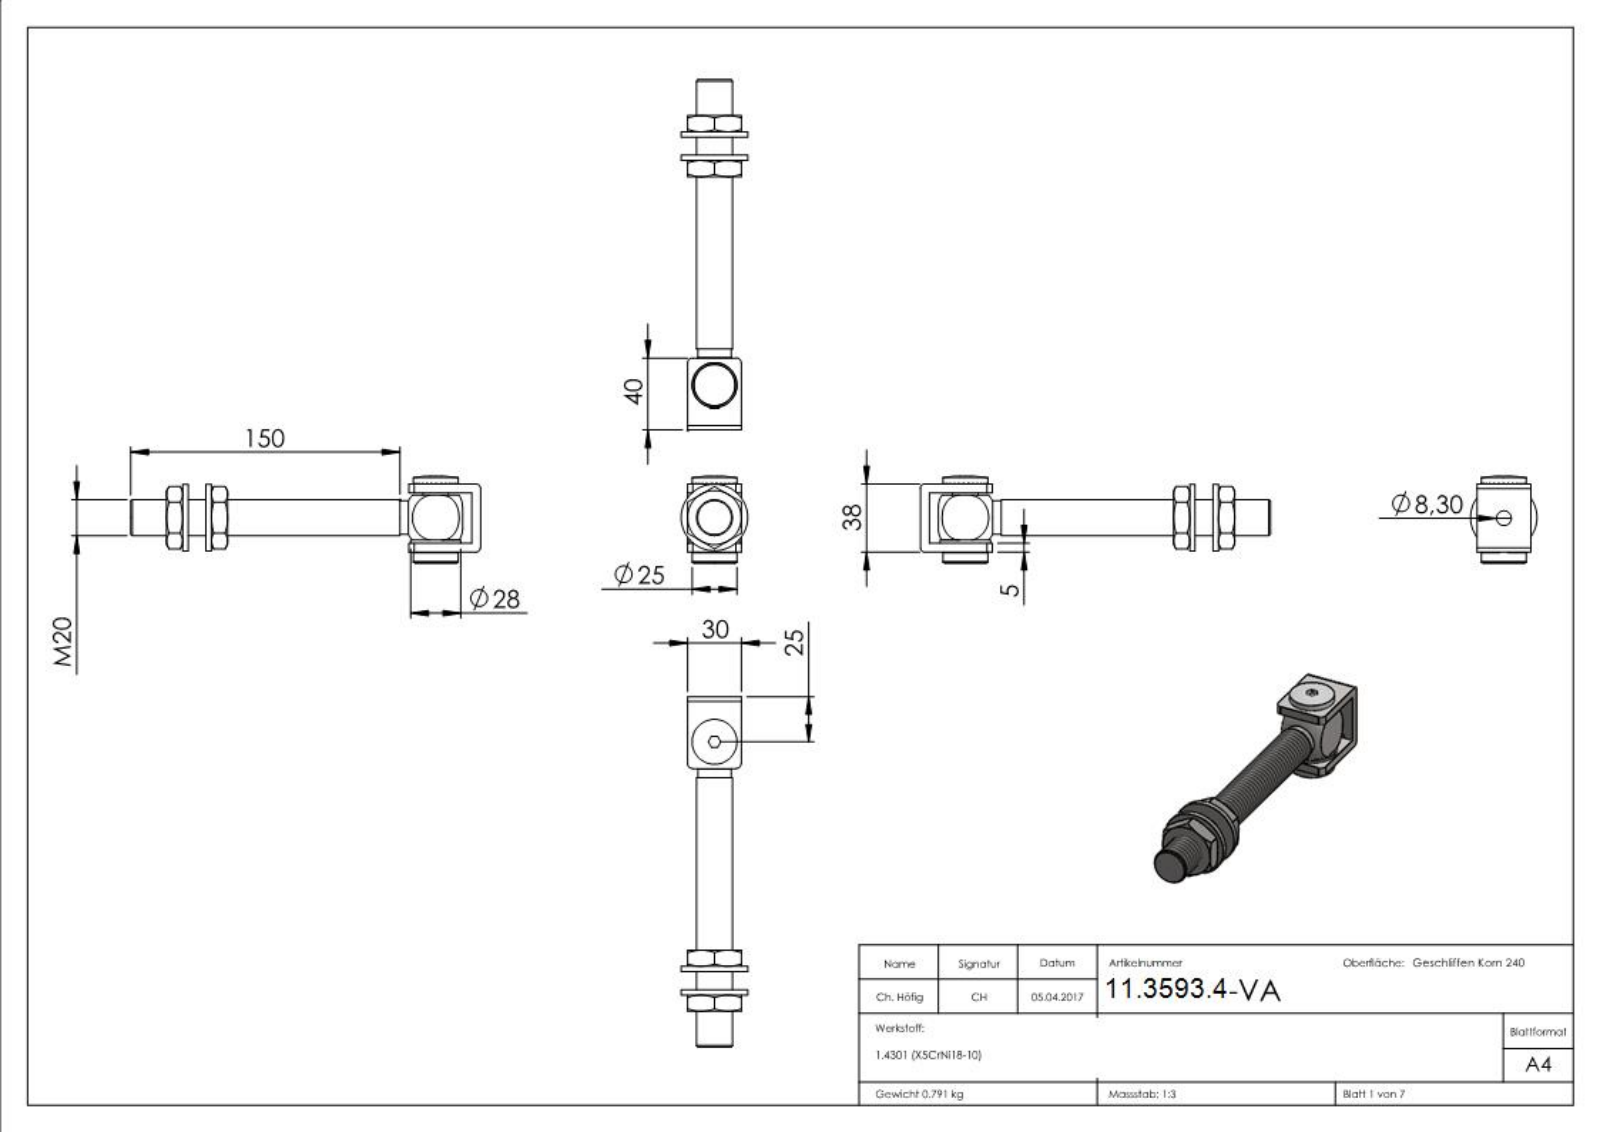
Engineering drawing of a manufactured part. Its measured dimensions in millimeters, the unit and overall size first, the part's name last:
Units: millimetres
Overall size (bounding box): 190.4 × 47.83 × 40
Round holes (diameter × count): ⌀6.8 ×1, ⌀8.2 ×1, ⌀9 ×1, ⌀15 ×1, ⌀17.5 ×1, ⌀18 ×1, ⌀21 ×1
Round bosses / shafts (diameter × count): ⌀40 ×1, ⌀26 ×1, ⌀25 ×1, ⌀20 ×1, ⌀14.5 ×1, ⌀8 ×1
Partial cylindrical surfaces — rounded edges, fillets, slot ends (radius × count): R1 ×2, R4 ×2, R4.4 ×2, R12.75 ×1
Main face-to-face distances: 30, 27.5, 3, 33, 5, 32.5, 2.5, 36, 25, 0.5
Hole centre spacings: 0.75
Volume: 99 443 mm³ · Surface area: 36 751 mm²
Bodies: 9 solids, 391 faces (247 planar, 28 cylindrical, 116 other)
Part name (STEP PRODUCT): 130-M20-VA; 130-M20-VA Teil3; 130-M20-VA Teil7; 130-M20-VA Teil5 (+5 more)
STEP written by: SolidWorks 2018 (CONFIG_CONTROL_DESIGN)
